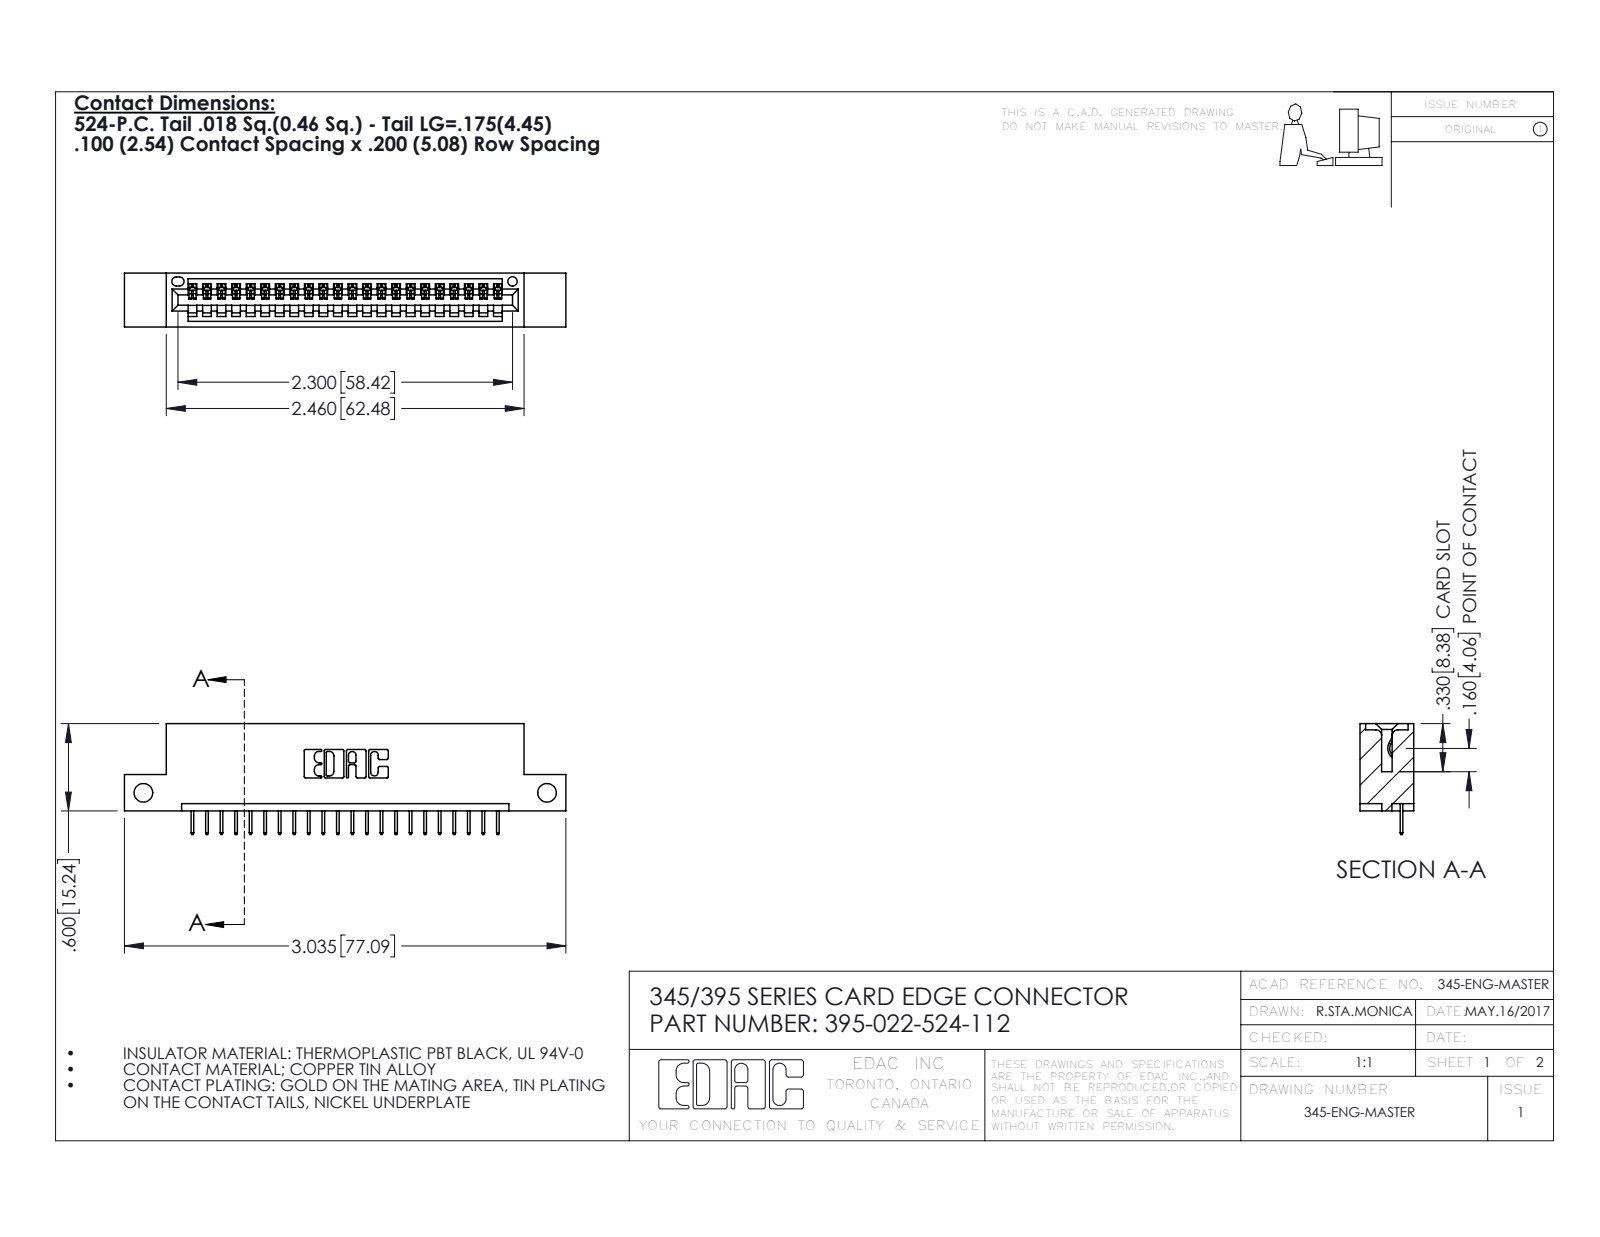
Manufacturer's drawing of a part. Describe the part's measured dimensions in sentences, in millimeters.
The part is named "345 Part_Flush Mounting Lugs - Side Mount; 395-022-524-112; 345-292-001_345-293-124". Its 3-D file was written by "SolidWorks 2016 (CONFIG_CONTROL_DESIGN)". It is 23 solids with 1490 faces: 1092 planar, 398 cylindrical and 0 other. Overall it measures 77.1 by 19.4 by 9.4 millimeters. Its volume is 6 980 cubic millimeters and its surface area 8 587 square millimeters. Round holes: 2 of diameter 3.3, 1 of diameter 1.6. Partial cylindrical surfaces (rounded edges, fillets, slot ends): 44 of radius 0.2, 22 of radius 0.3, 6 of radius 0.2, 6 of radius 0.8, 3 of radius 0.7, 2 of radius 0.8, 2 of radius 1, 1 of radius 0.4. The main face-to-face distances are 7.6, 1.8, 9.4, 5.1, 2.5, 6.9, 0.6, 5.7, 1.8, 3.8. The hole center spacings are 70.5.
